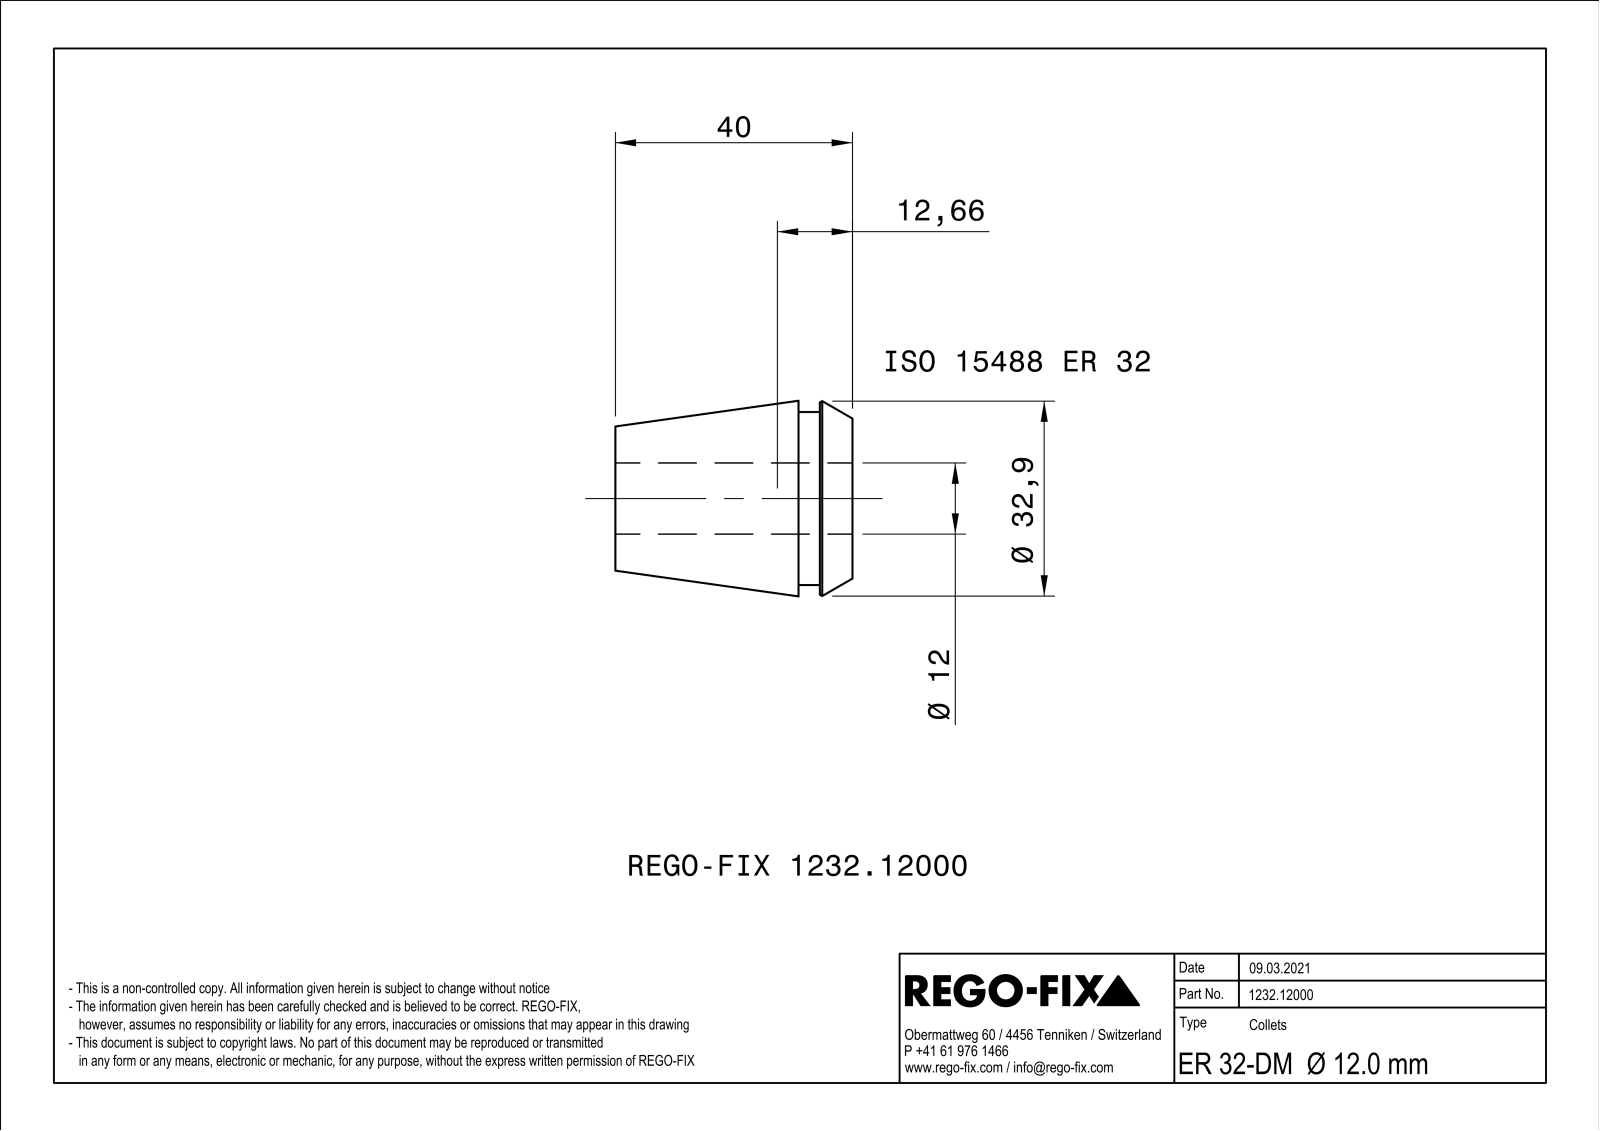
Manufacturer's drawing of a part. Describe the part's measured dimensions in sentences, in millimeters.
The part is named "NOCUT". Its 3-D file was written by "SIEMENS PLM Software Solid Edge ST10 (AUTOMOTIVE_DESIGN)". It is 1 solid with 154 faces: 80 planar, 9 cylindrical and 65 other. Overall it measures 40 by 32.98 by 32.98 millimeters. Its volume is 17 953 cubic millimeters and its surface area 13 326 square millimeters. Round holes: 1 of diameter 12. Round bosses or shafts: 1 of diameter 29.2. The main face-to-face distances are 1, 40, 9.1, 30.9, 5.5, 3.6, 34.5, 16, 10.5, 6.9.
